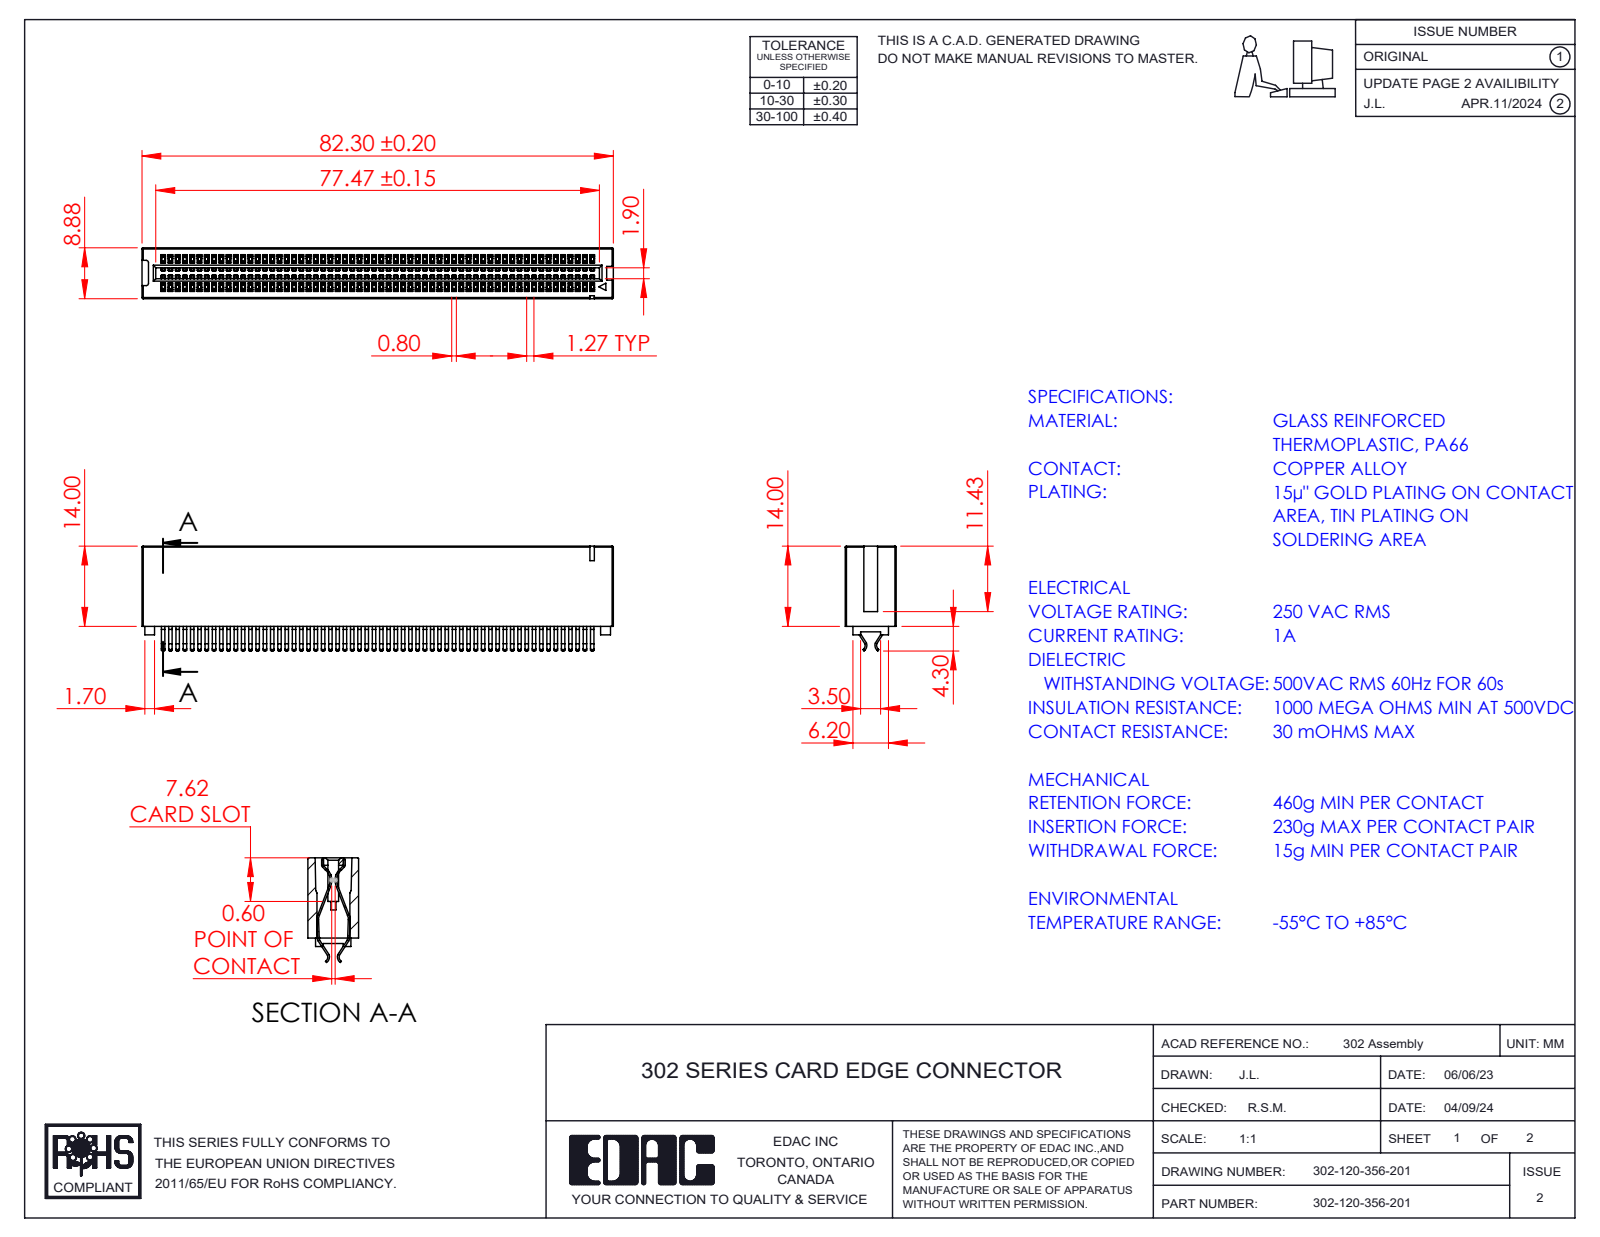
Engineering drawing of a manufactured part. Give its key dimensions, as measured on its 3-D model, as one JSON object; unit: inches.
{"part_name": "HSG_Vertical HSG; Contact_302-290-X56; 302-120-356-201", "step_written_by": "SolidWorks 2023 (CONFIG_CONTROL_DESIGN)", "units": "inches", "bodies": {"solids": 121, "faces": 5766, "planar": 3829, "cylindrical": 1933, "other": 4}, "overall_size": [3.24, 0.72, 0.35], "volume_in3": 0.383, "surface_area_in2": 28.11, "partial_cylinders_radius": [[0.008, 368], [0.004, 2], [0.016, 2], [0.016, 2], [0.037, 2], [0.041, 2], [0.048, 2], [0.049, 2]], "face_to_face_distances": [0.35, 0.05, 0.1, 0.15, 0.2, 0.3, 0.25, 0.35, 0.4, 0.5]}
